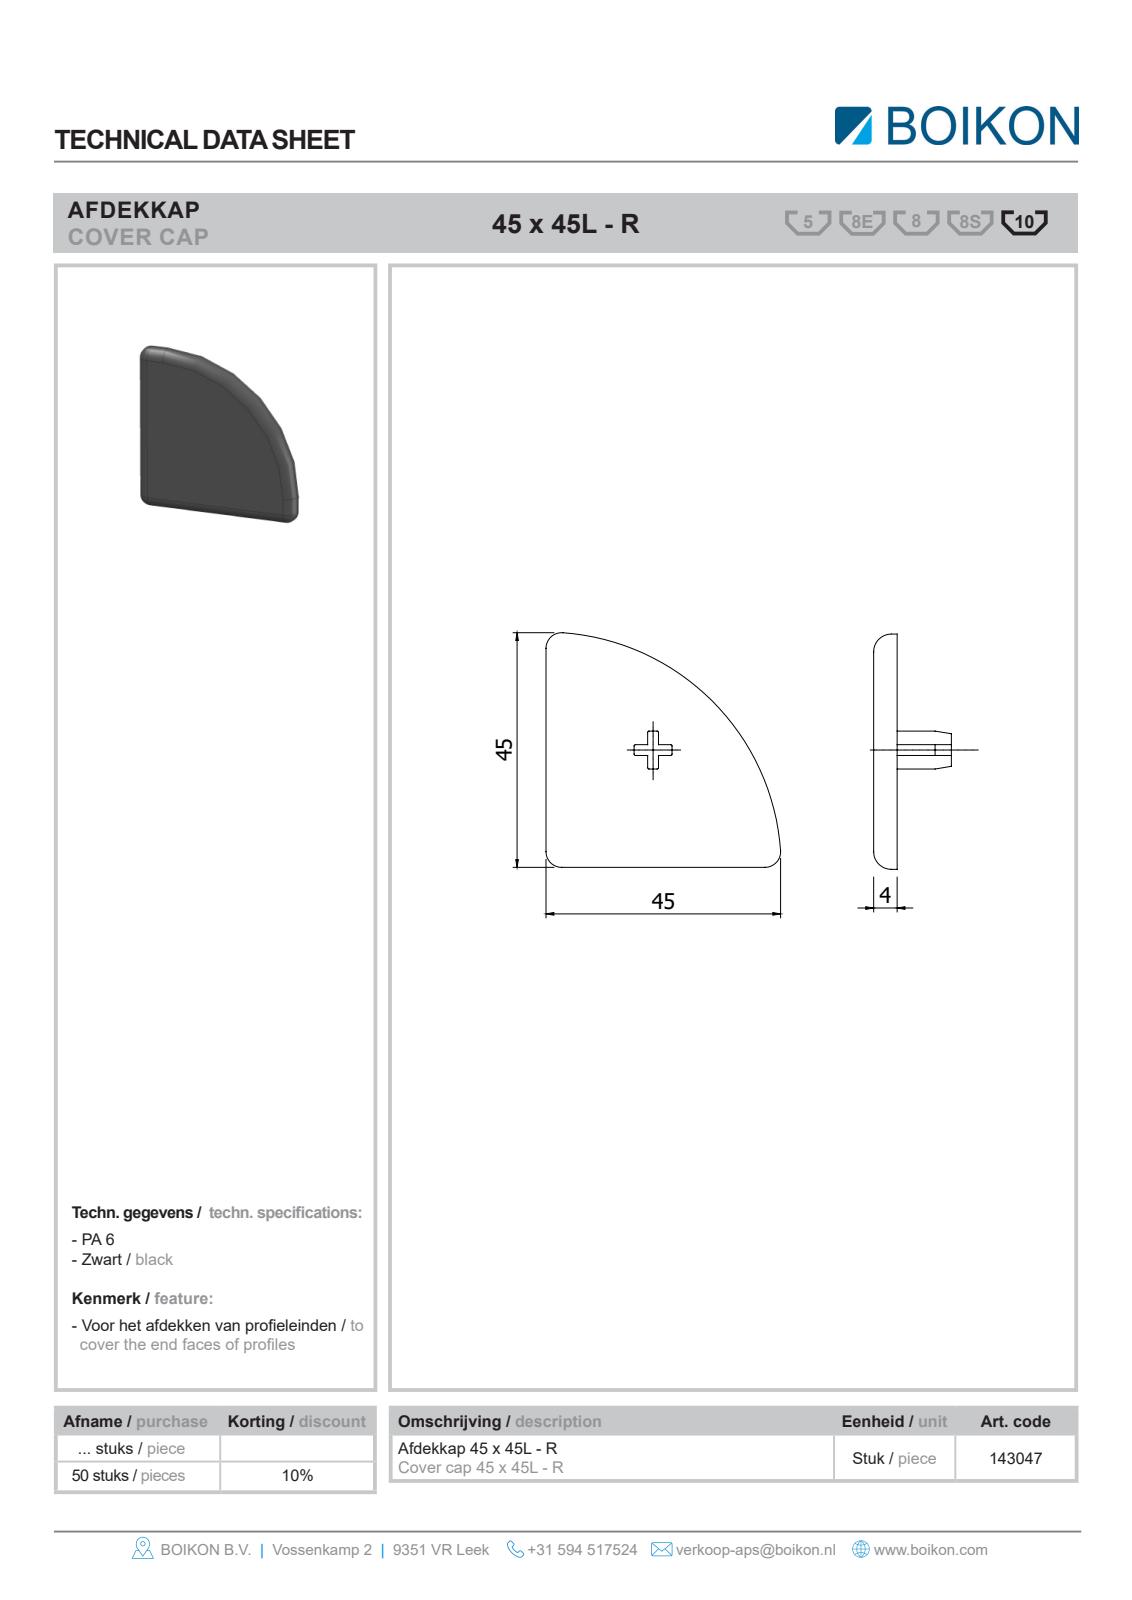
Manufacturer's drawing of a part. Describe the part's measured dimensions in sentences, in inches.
The part is named "Root; 143047Afdekkap 45x45L-RBOIKON0". Its 3-D file was written by "HiCAD 2013 1802.4 Build 509 (AUTOMOTIVE_DESIGN)". It is 1 solid with 18 faces: 6 planar, 8 cylindrical and 4 other. Overall it measures 1.772 by 1.772 by 0.157 inches. Its volume is 0.401 cubic inches and its surface area 5.991 square inches. Partial cylindrical surfaces (rounded edges, fillets, slot ends): 7 of radius 0.118, 1 of radius 1.476. The main face-to-face distances are 0.157, 1.772.
